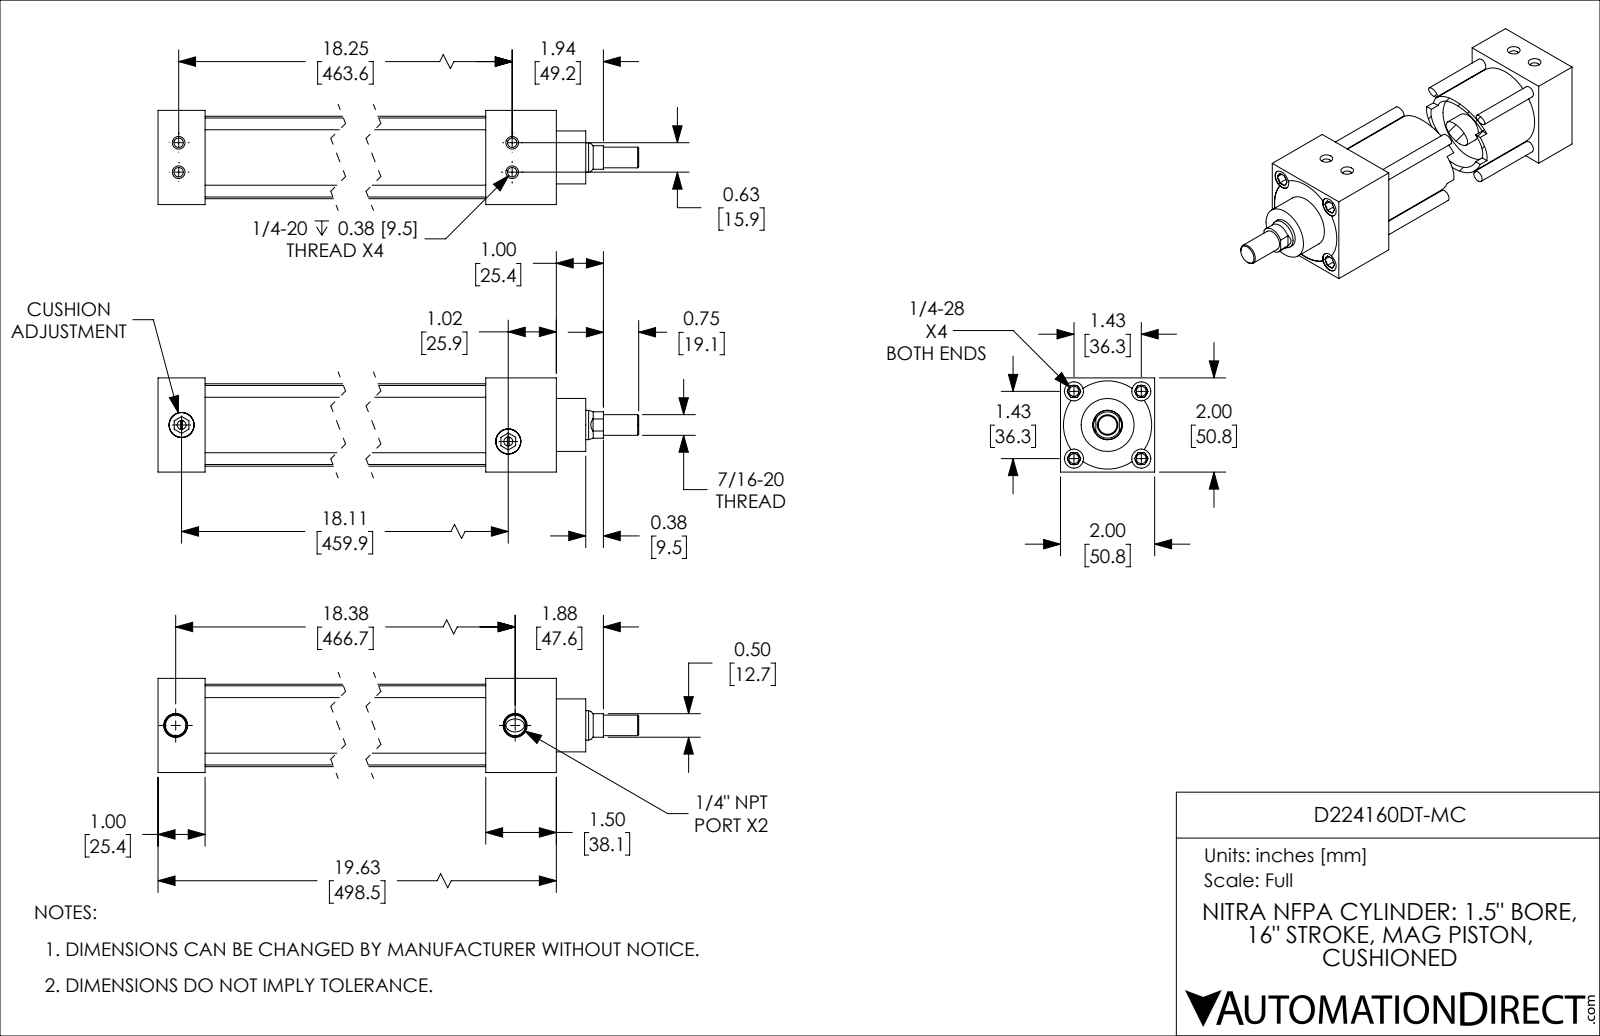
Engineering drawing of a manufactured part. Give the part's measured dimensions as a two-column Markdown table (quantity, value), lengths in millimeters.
| quantity | value |
| --- | --- |
| part name | D224160DT-MC_CUSHION; D224160DT-MC; D224160DT-MC_PISTON_KK1; D224160DT-MC_BODY |
| STEP written by | SolidWorks 2019 (CONFIG_CONTROL_DESIGN) |
| units | millimeters |
| bodies | 4 solids, 251 faces (90 planar, 81 cylindrical, 80 other) |
| overall size | 542.9 × 50.8 × 50.8 |
| volume | 514 900 mm³ |
| surface area | 209 000 mm² |
| round holes (diameter × count) | 5.1 × 4, 5.4 × 4, 10.3 × 4, 4.8 × 2, 11.1 × 2, 13.5 × 2, 15.9 × 1, 38.1 × 1 |
| round bosses / shafts (diameter × count) | 6.4 × 4, 13.5 × 2, 44.5 × 1, 38.1 × 1, 28.6 × 1, 15.8 × 1, 11.1 × 1 |
| partial cylindrical surfaces (radius × count) | 7.1 × 1, 23.8 × 1 |
| main face-to-face distances | 50.8, 25.4, 460.4, 435, 54, 498.3, 472.9, 38, 28.6, 406.4 |
| hole center spacings | 8.1, 25.7, 36.3, 15.9, 51.4, 463.6, 463.8, 465.2 |
